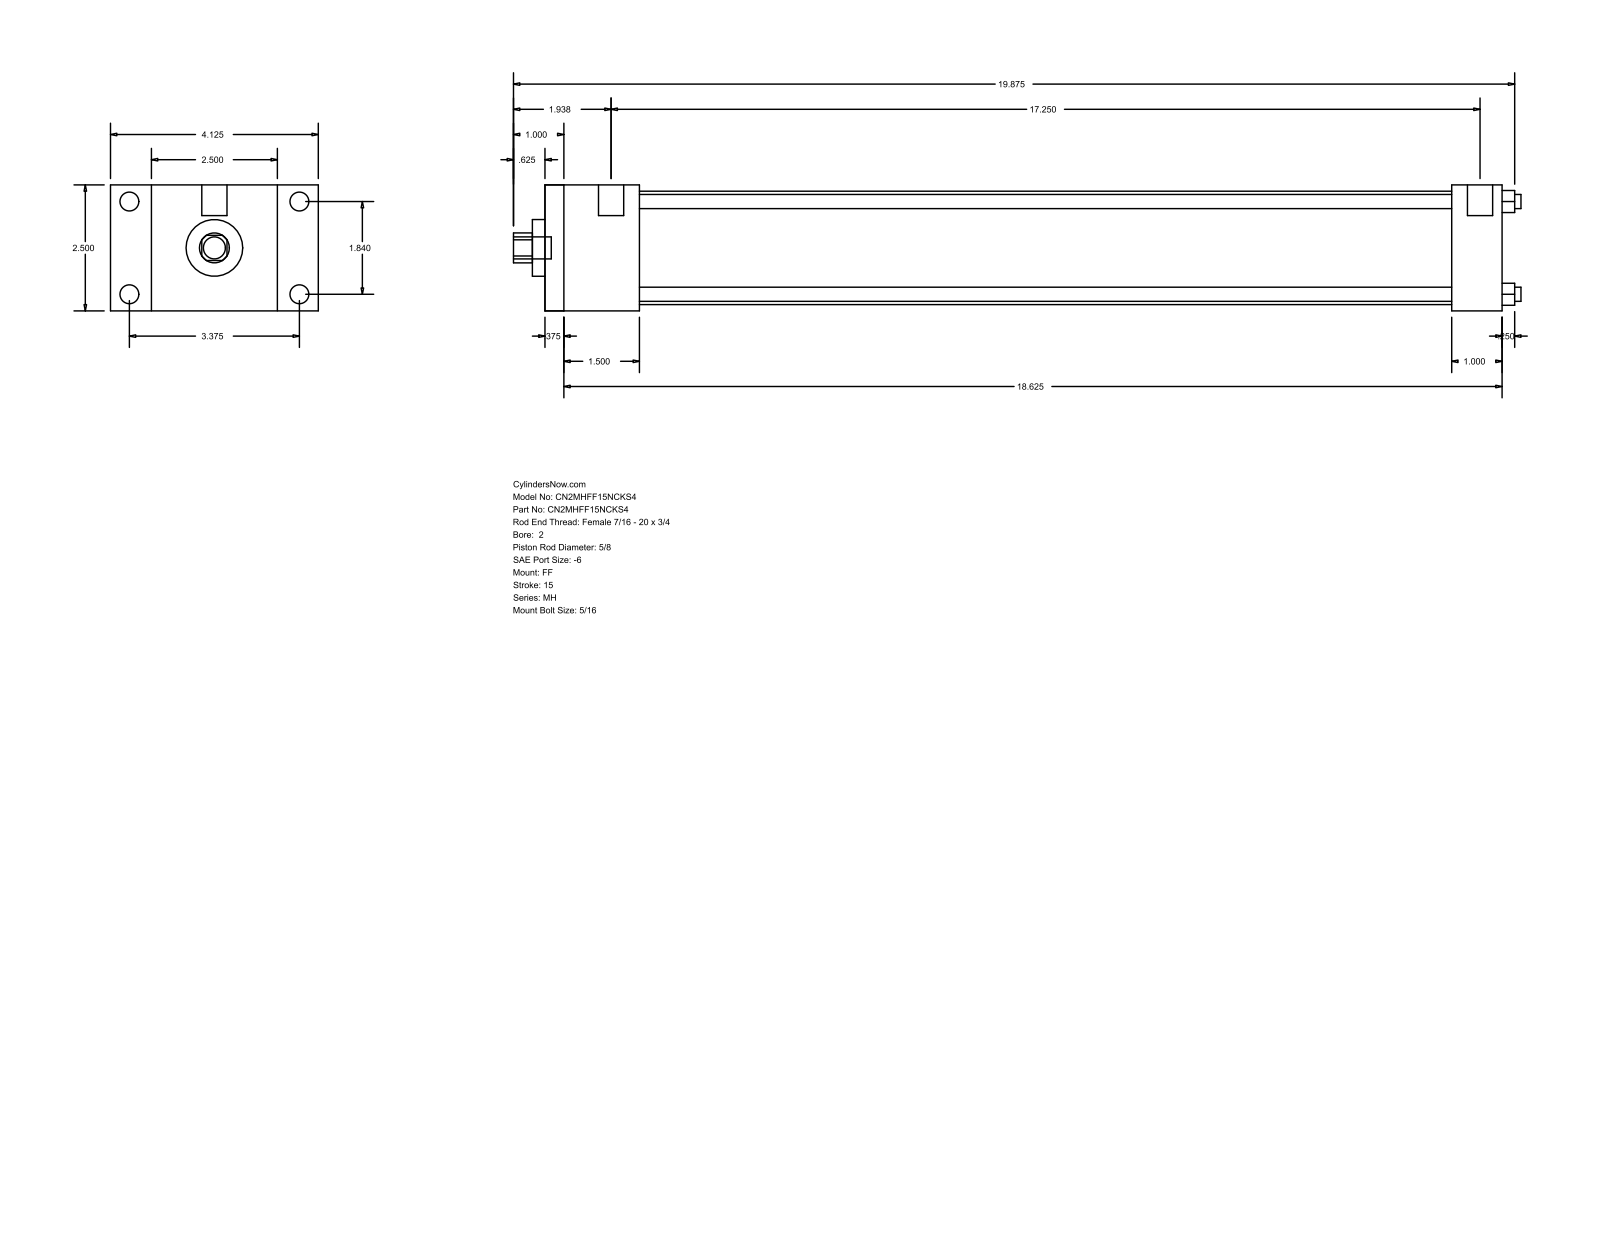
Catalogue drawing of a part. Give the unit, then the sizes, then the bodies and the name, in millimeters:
Units: millimetres
Overall size (bounding box): 508 × 104.78 × 63.5
Round holes (diameter × count): ⌀7.14 ×4, ⌀15.88 ×1, ⌀28.57 ×1, ⌀57.15 ×1
Round bosses / shafts (diameter × count): ⌀9.53 ×4, ⌀5.56 ×4, ⌀12.7 ×2, ⌀11.11 ×1
Partial cylindrical surfaces — rounded edges, fillets, slot ends (radius × count): R7.54 ×1
Main face-to-face distances: 63.5, 482.6, 9.52, 473.08, 38.1, 47.62, 457.19, 447.67, 409.57, 434.98
Hole centre spacings: 33.05, 46.74, 66.1
Bodies: 0 solids, 92 faces (64 planar, 28 cylindrical, 0 other)
Part name (STEP PRODUCT): MH_FF__0200_0.625
STEP written by: GSSL Pune (CONFIG_CONTROL_DESIGN)
